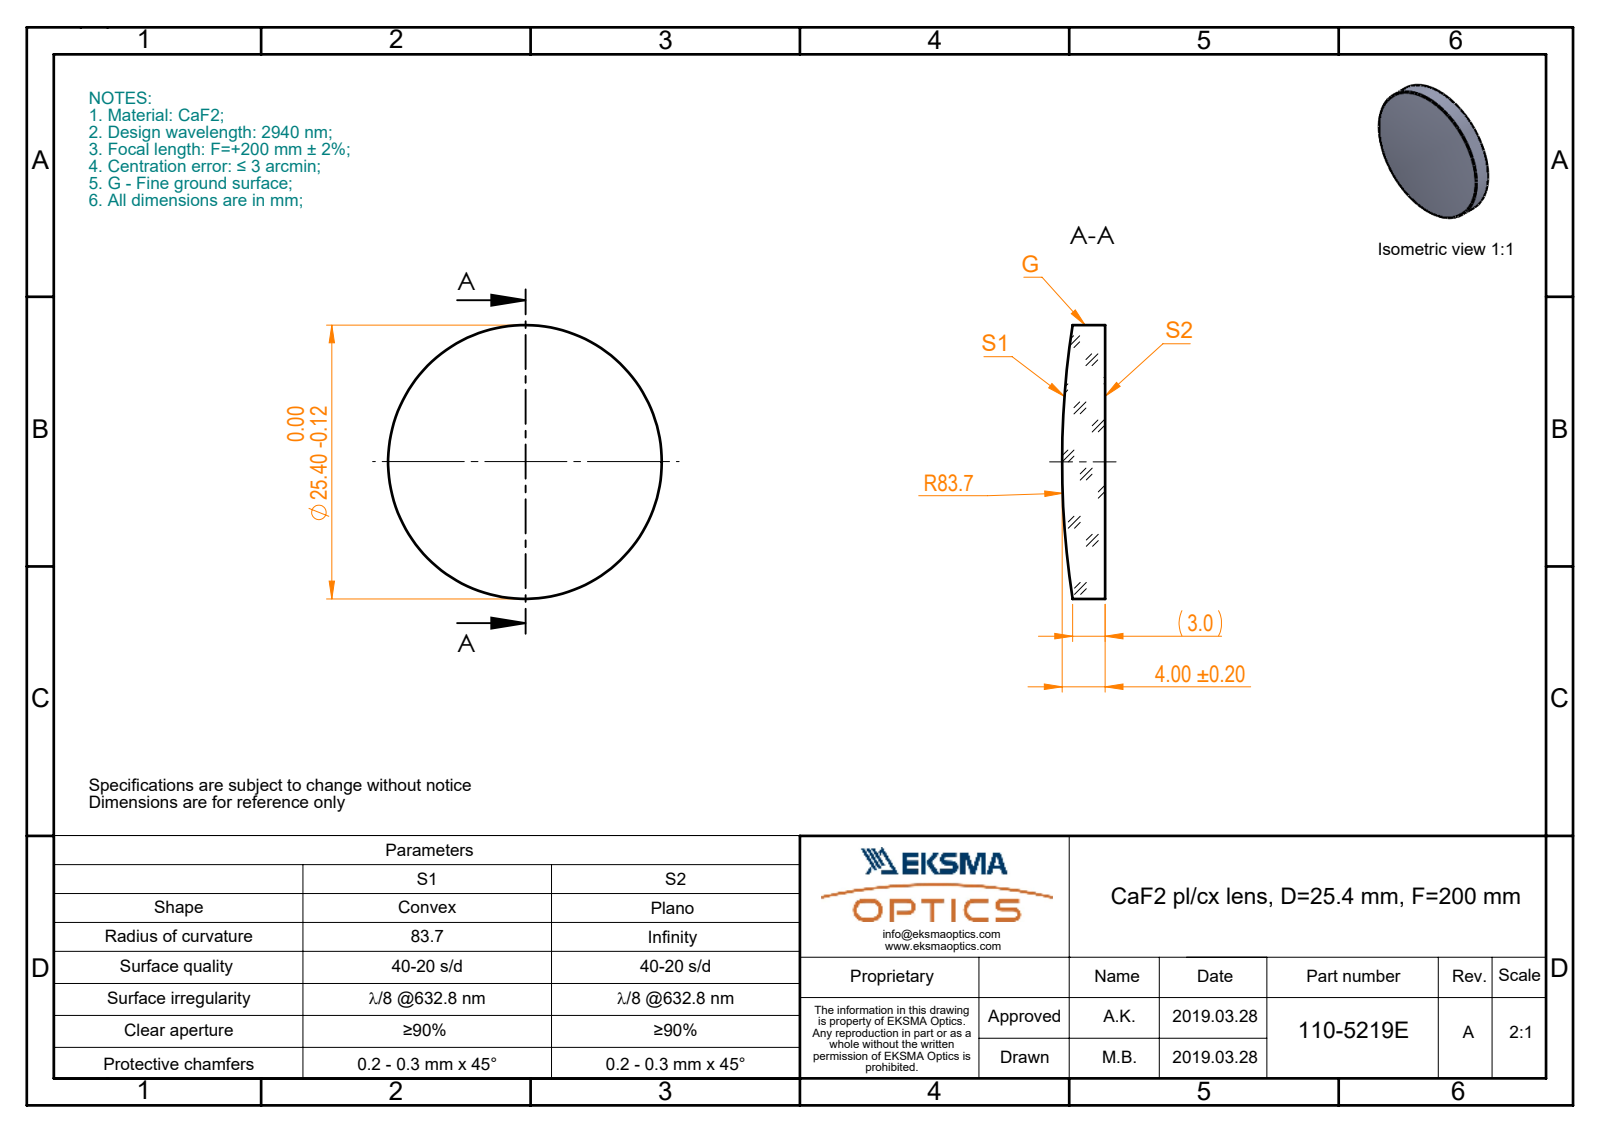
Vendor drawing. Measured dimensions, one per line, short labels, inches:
name: 110-5219E CaF2 pl-cx 25.4 F200
written by: SolidWorks 2017 (CONFIG_CONTROL_DESIGN)
unit: in
bodies: 1 solid, 5 faces (1 planar, 2 cylindrical, 2 other)
size: 1 × 1 × 0.157
volume: 0.109 in³; area: 1.95 in²
bosses: 1× ⌀1
